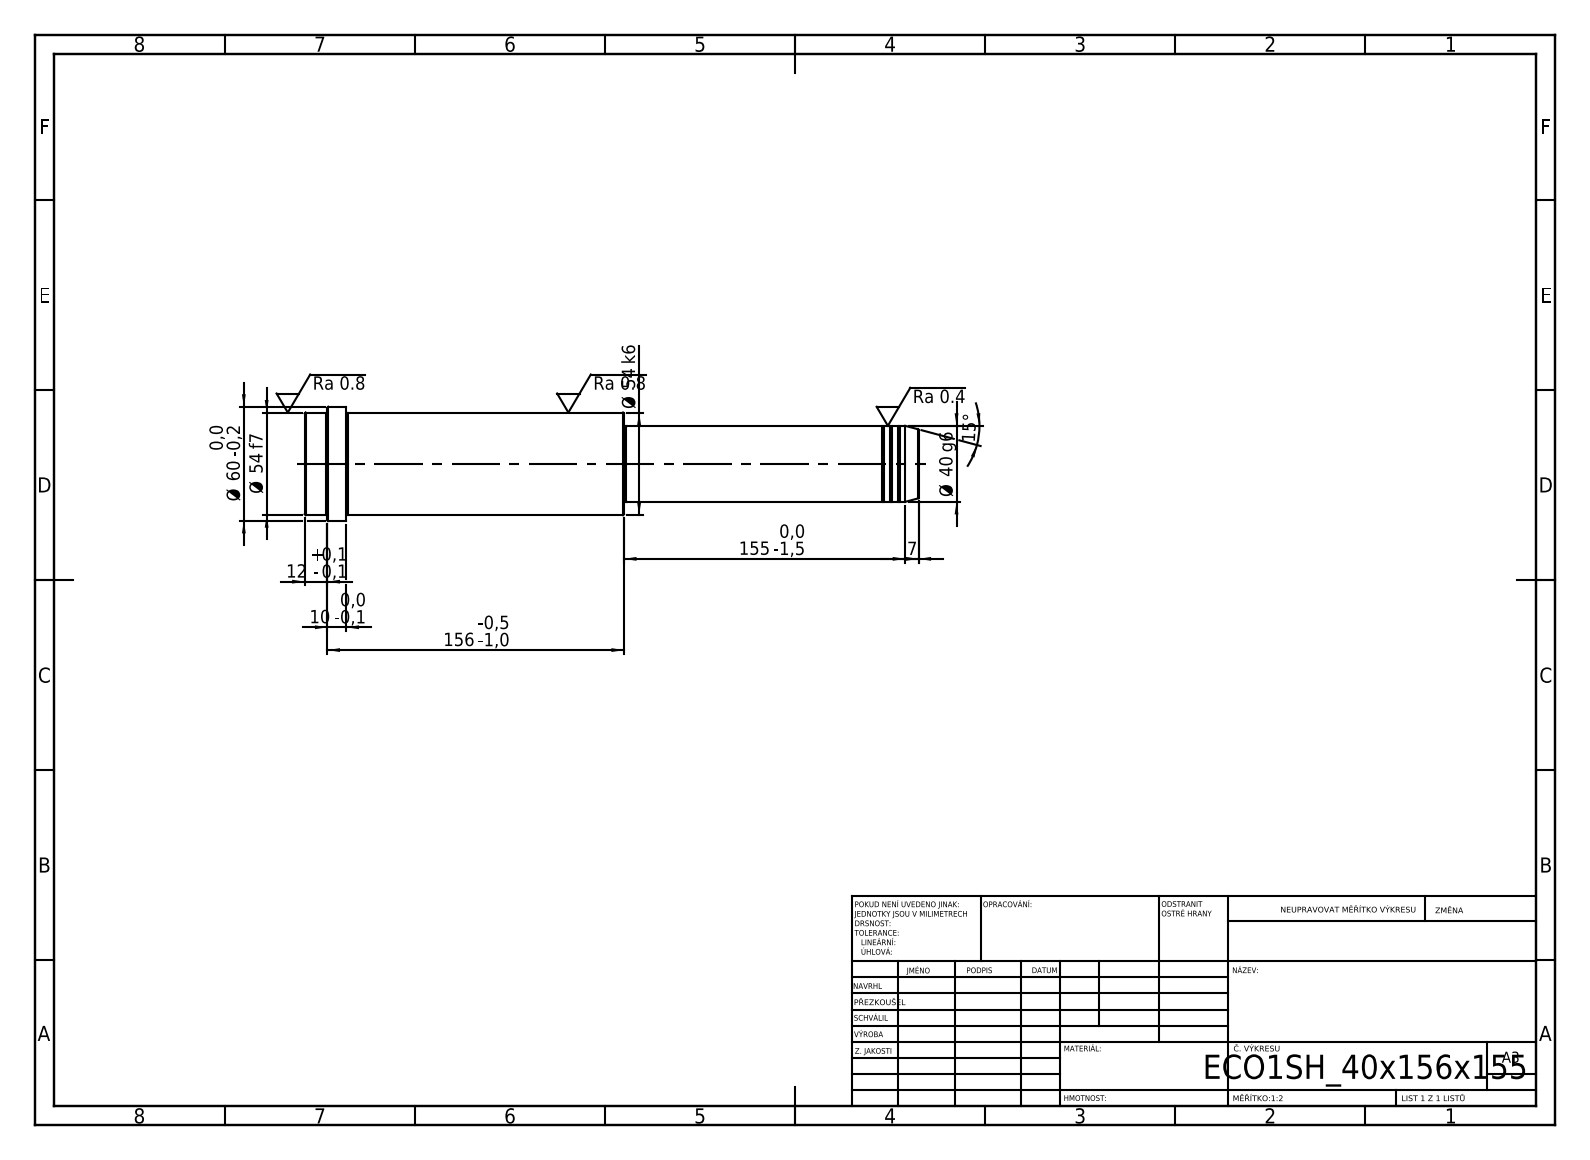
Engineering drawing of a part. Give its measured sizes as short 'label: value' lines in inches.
written by: SolidWorks 2019 (CONFIG_CONTROL_DESIGN)
unit: in
bodies: 1 solid, 52 faces (6 planar, 16 cylindrical, 30 other)
size: 12.717 × 2.362 × 2.362
volume: 35.62 in³; area: 83.59 in²
bosses: 1× ⌀2.362, 1× ⌀2.126, 1× ⌀1.575, 1× ⌀1.535
face distances: 6.614, 6.102, 12.717, 11.85, 5.748, 0.866, 12.244, 6.142, 0.394, 0.472
